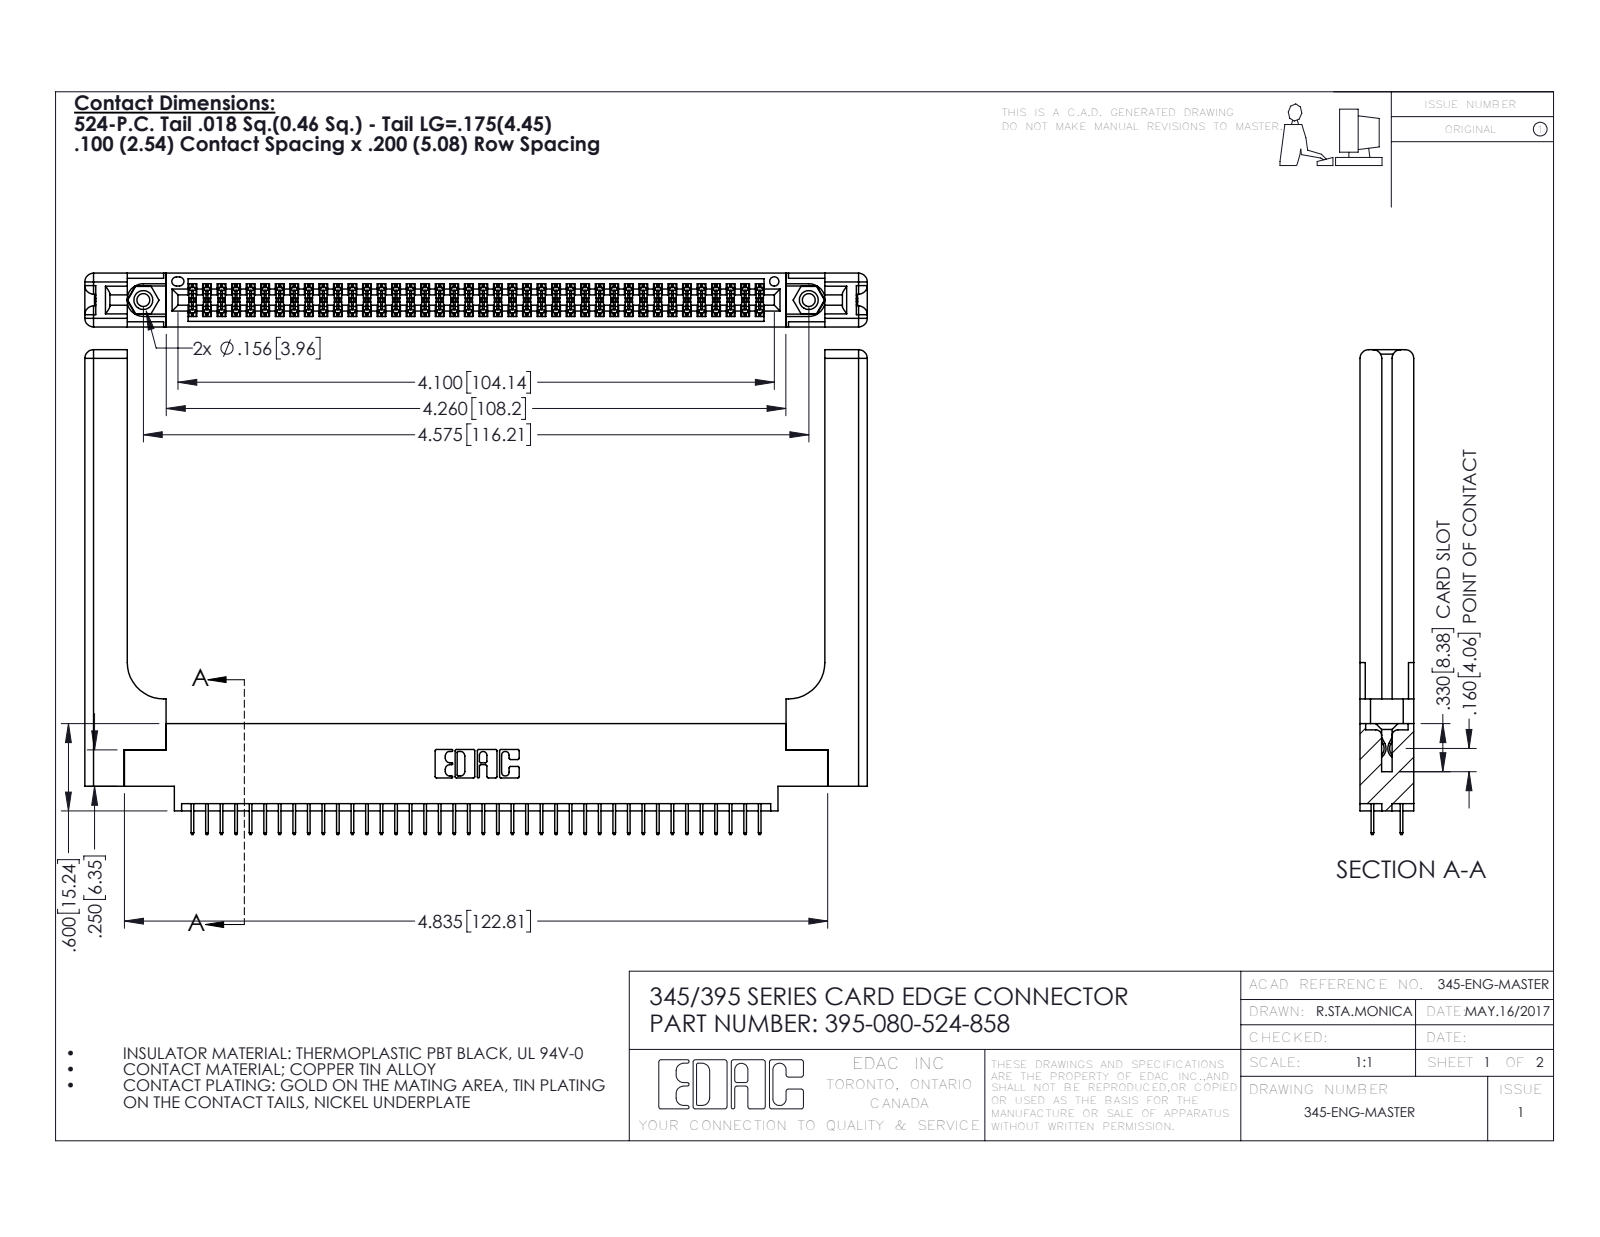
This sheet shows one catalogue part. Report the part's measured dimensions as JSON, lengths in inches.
{"part_name": "345-292-001_345-293-124; 345 Part_0.170 Offset - 0.156 Dia-TH; 345-250-001_345-250-001-102; 345-220-058_345-220-058 (+1 more)", "step_written_by": "SolidWorks 2016 (CONFIG_CONTROL_DESIGN)", "units": "inches", "bodies": {"solids": 85, "faces": 4706, "planar": 3352, "cylindrical": 1294, "other": 60}, "overall_size": [5.379, 3.332, 0.37], "volume_in3": 1.312, "surface_area_in2": 37.34, "round_holes": [[0.089, 2], [0.125, 2], [0.156, 2], [0.064, 1]], "round_bosses_or_shafts": [[0.155, 2]], "partial_cylinders_radius": [[0.006, 120], [0.01, 22], [0.06, 16], [0.007, 6], [0.031, 6], [0.026, 3], [0.014, 2], [0.019, 2]], "face_to_face_distances": [0.37, 0.072, 0.298, 0.2, 0.098, 0.272, 0.025, 0.225, 0.148, 0.15], "hole_center_spacings": [0.27, 4.339, 4.575]}
